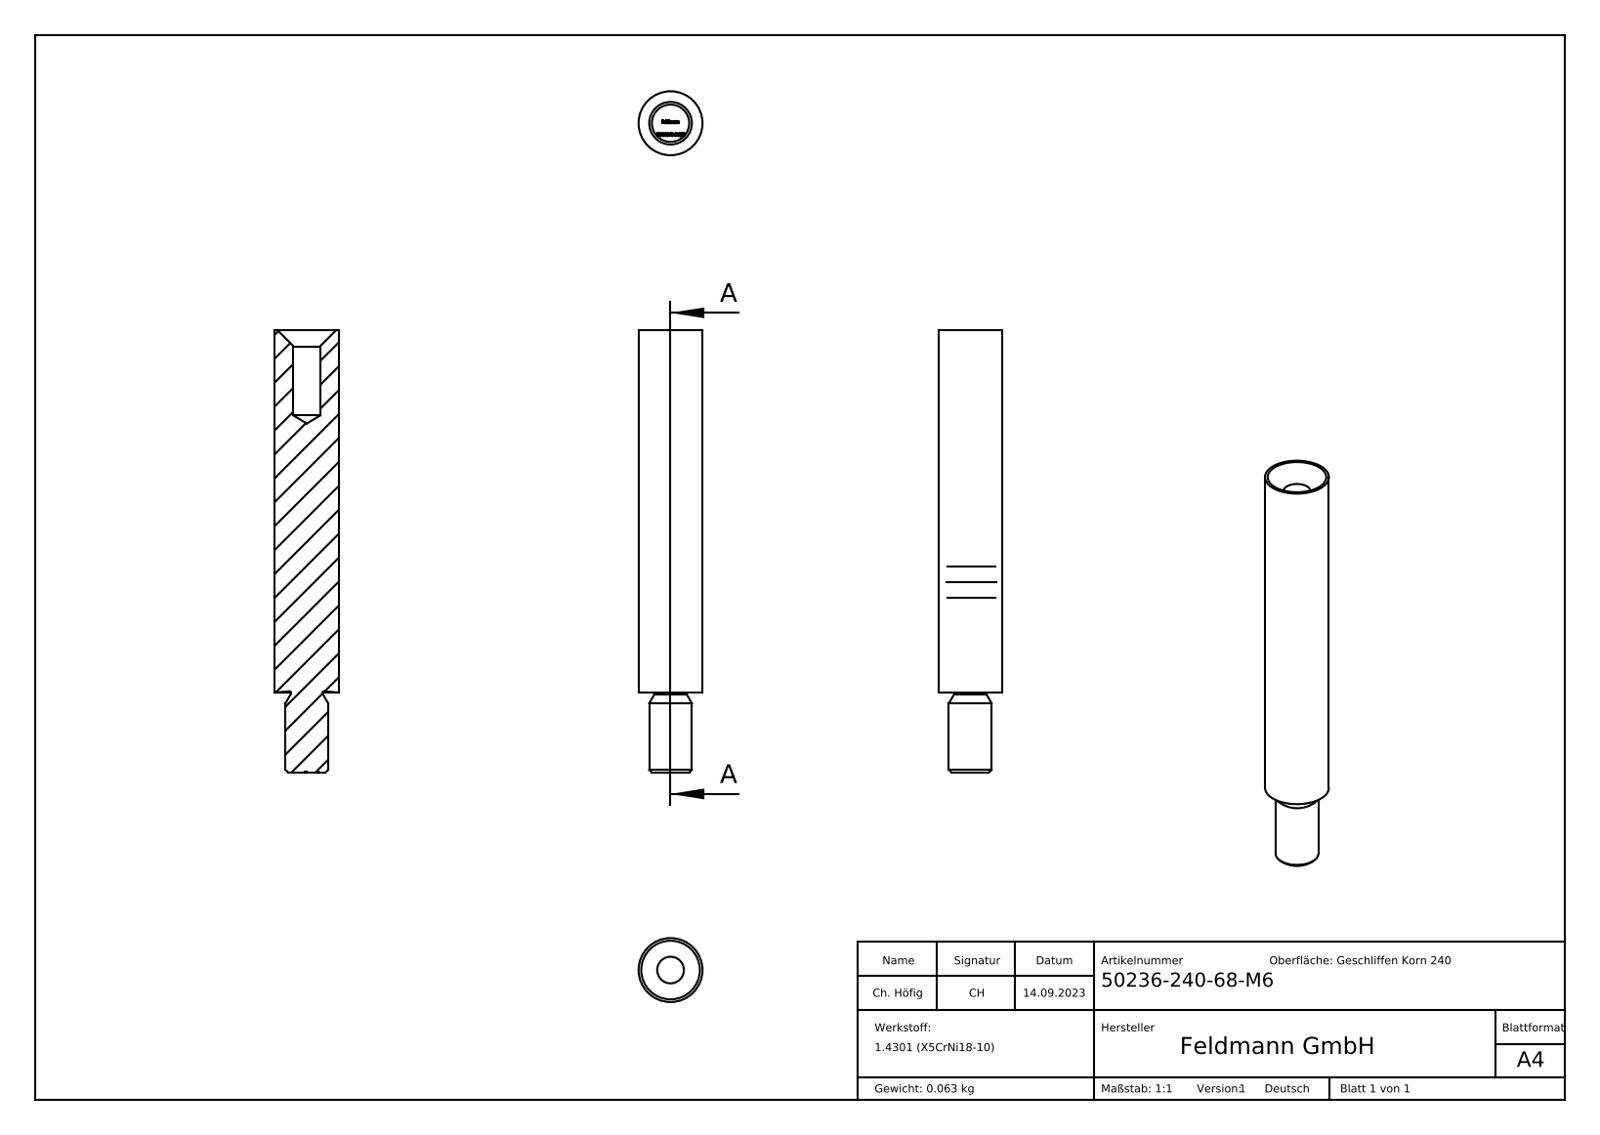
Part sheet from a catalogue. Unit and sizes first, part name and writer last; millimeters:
Units: millimetres
Overall size (bounding box): 83 × 12 × 12
Round holes (diameter × count): ⌀5 ×1
Round bosses / shafts (diameter × count): ⌀12 ×1, ⌀8 ×1
Main face-to-face distances: 83, 82.9, 0.77, 1.29, 2.38, 2.39, 0.72, 1.55, 2.44, 0.57
Volume: 7 983 mm³ · Surface area: 3 426 mm²
Bodies: 1 solid, 269 faces (157 planar, 3 cylindrical, 109 other)
Part name (STEP PRODUCT): 50236-240-68-M6
STEP written by: SolidWorks 2018 (CONFIG_CONTROL_DESIGN)
